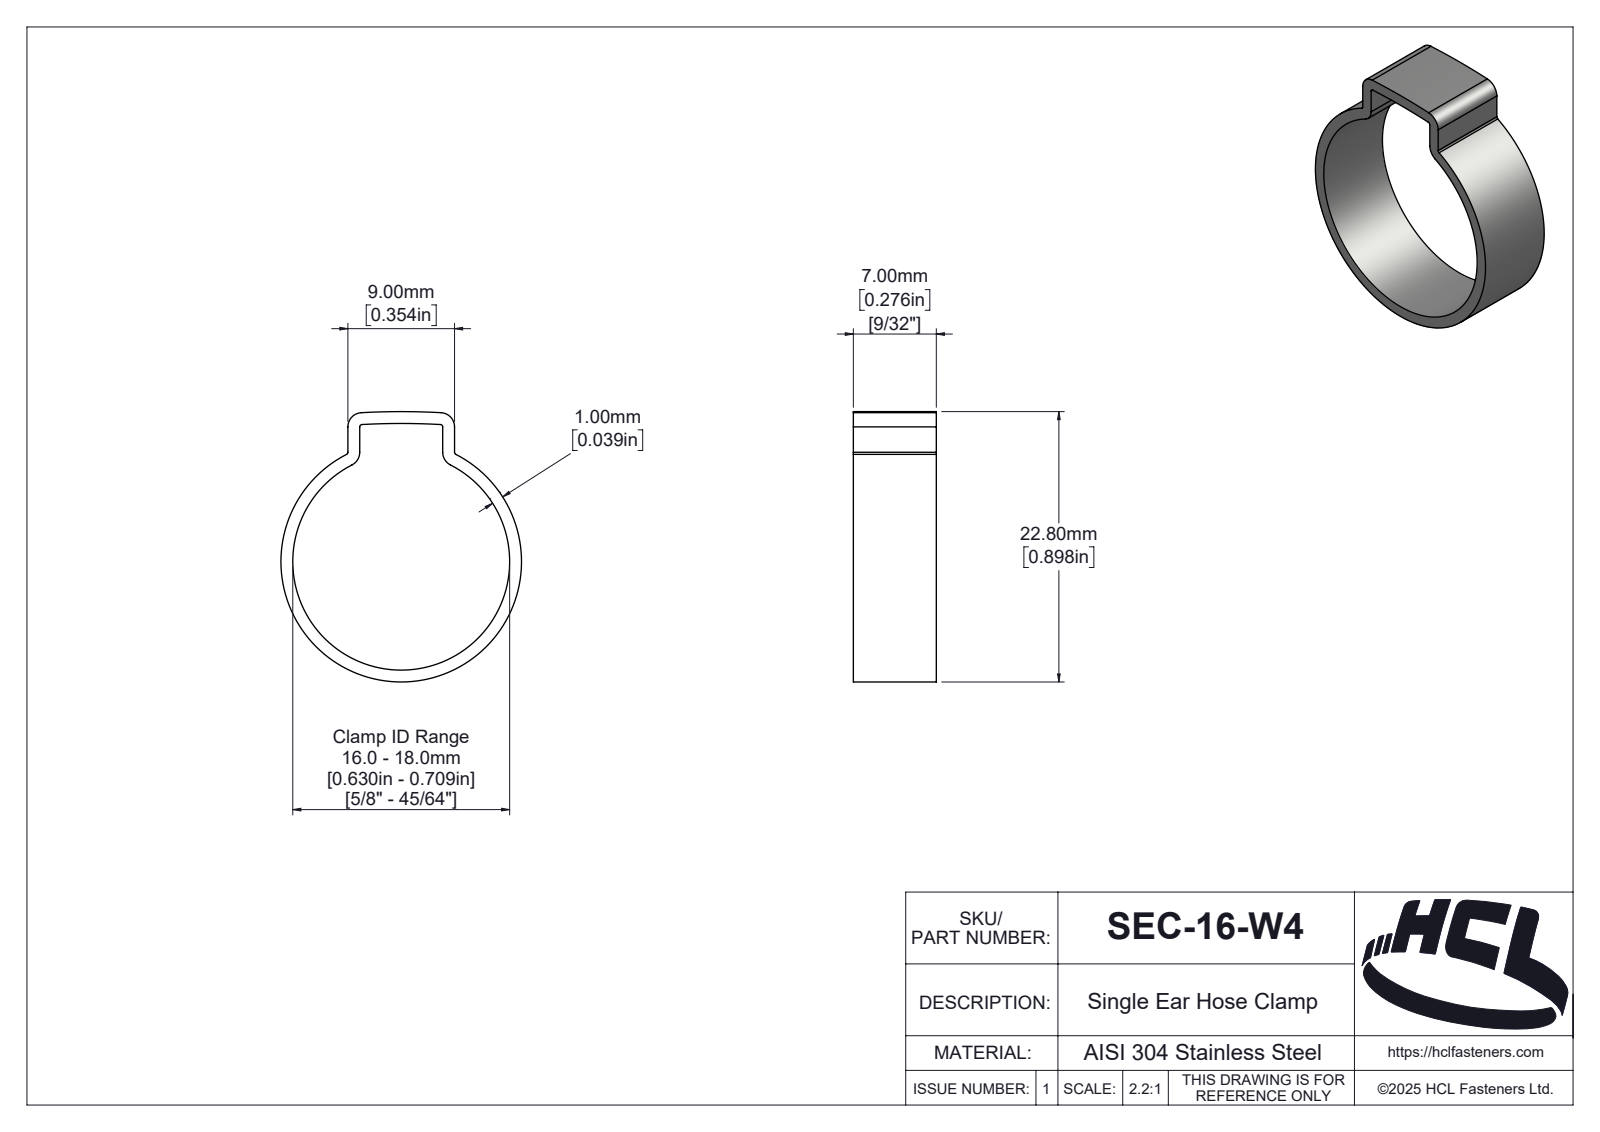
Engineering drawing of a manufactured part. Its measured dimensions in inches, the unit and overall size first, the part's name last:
Units: inches
Overall size (bounding box): 0.898 × 0.799 × 0.276
Round holes (diameter × count): ⌀0.72 ×1
Round bosses / shafts (diameter × count): ⌀0.799 ×1
Partial cylindrical surfaces — rounded edges, fillets, slot ends (radius × count): R0.008 ×4, R0.047 ×4, R0.008 ×1, R0.032 ×1, R0.04 ×1, R0.042 ×1, R0.05 ×1, R0.071 ×1
Main face-to-face distances: 0.276, 0.039, 0.315, 0.354, 0.167, 0.127, 0.148, 0.188, 0.172, 0.133
Volume: 0.028 in³ · Surface area: 1.646 in²
Bodies: 1 solid, 123 faces (8 planar, 66 cylindrical, 49 other)
Part name (STEP PRODUCT): SEC-16-W4
STEP written by: SolidWorks 2025 (AUTOMOTIVE_DESIGN)
